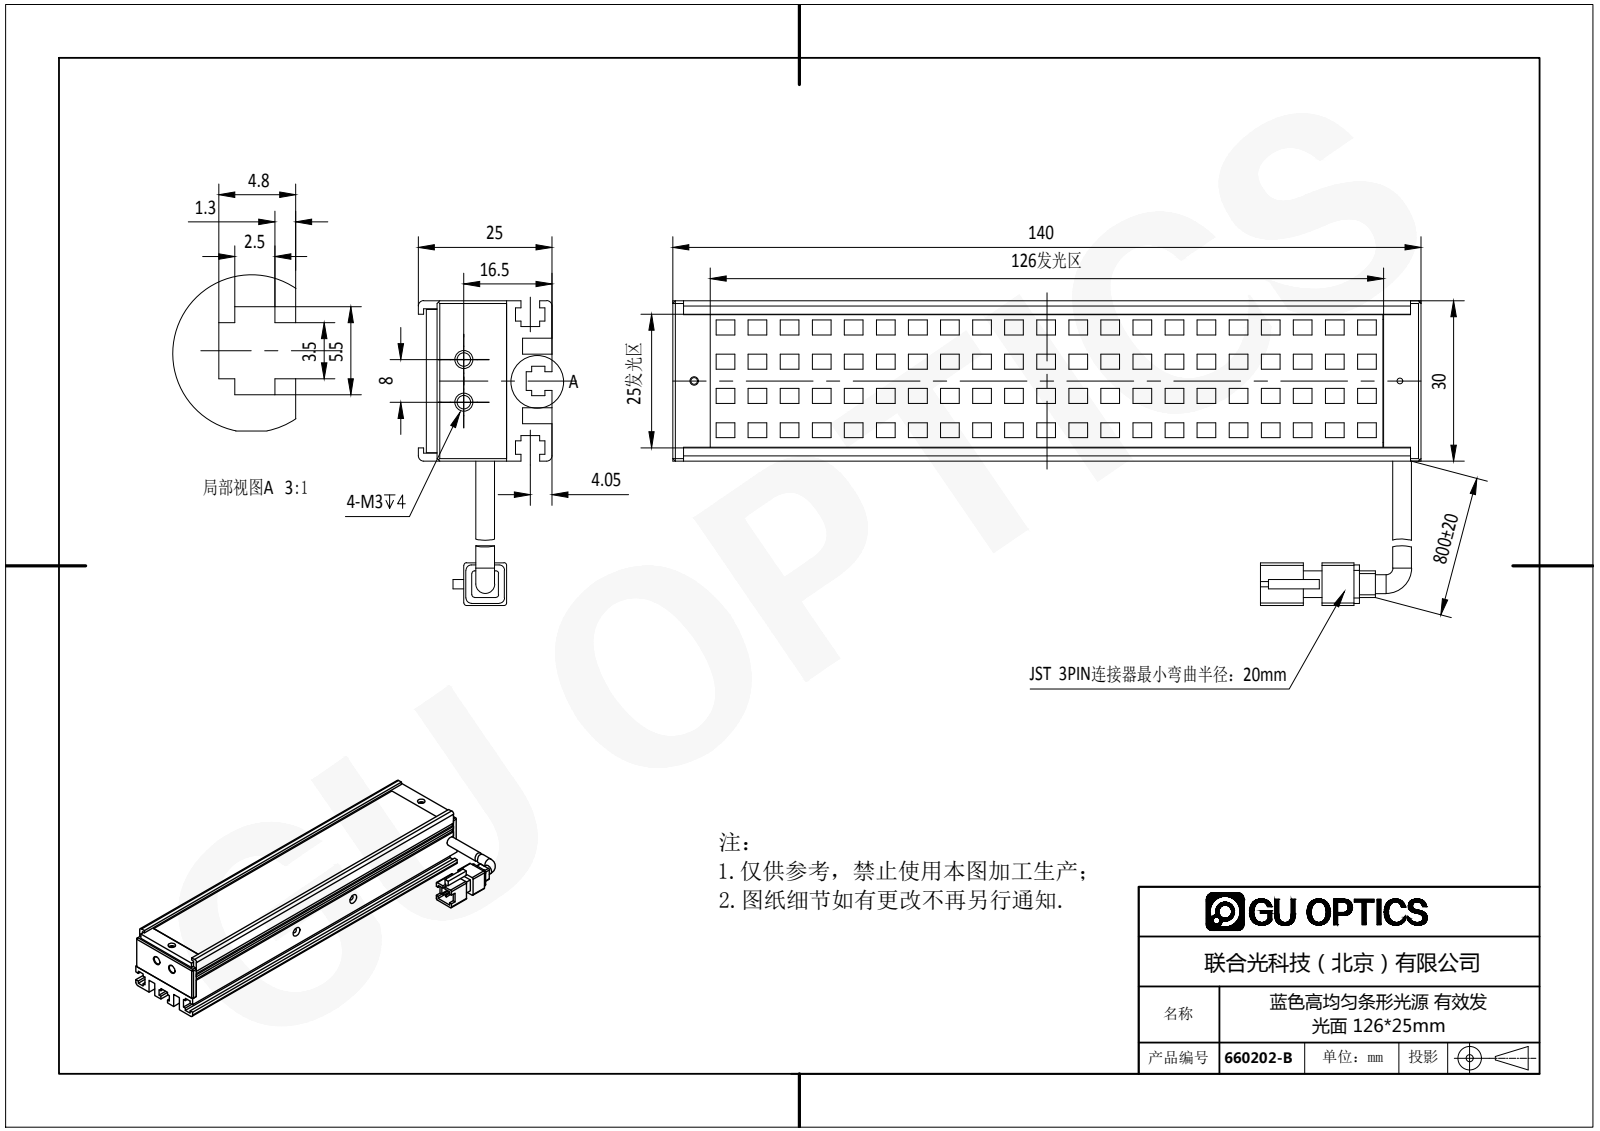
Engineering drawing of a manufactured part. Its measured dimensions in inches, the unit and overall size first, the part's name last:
Units: inches
Overall size (bounding box): 5.512 × 2.244 × 0.984
Round holes (diameter × count): ⌀0.063 ×5, ⌀0.059 ×2, ⌀0.067 ×2, ⌀0.098 ×2, ⌀0.11 ×2, ⌀0.118 ×2, ⌀0.043 ×1, ⌀0.049 ×1, ⌀0.079 ×1
Round bosses / shafts (diameter × count): ⌀0.138 ×2
Partial cylindrical surfaces — rounded edges, fillets, slot ends (radius × count): R0.039 ×12, R0.02 ×8, R0.065 ×1
Main face-to-face distances: 0.039, 0.512, 0.079, 0.098, 0.118, 0.374, 1.083, 0.177, 0.335, 0.846
Hole centre spacings: 5.197, 0.276, 2.008, 2.025, 3.189, 3.2, 5.204, 0.315
Volume: 3.043 in³ · Surface area: 78.16 in²
Bodies: 6 solids, 864 faces (678 planar, 83 cylindrical, 103 other)
Part name (STEP PRODUCT): 660202-B
STEP written by: SolidWorks 2016 (AUTOMOTIVE_DESIGN)
